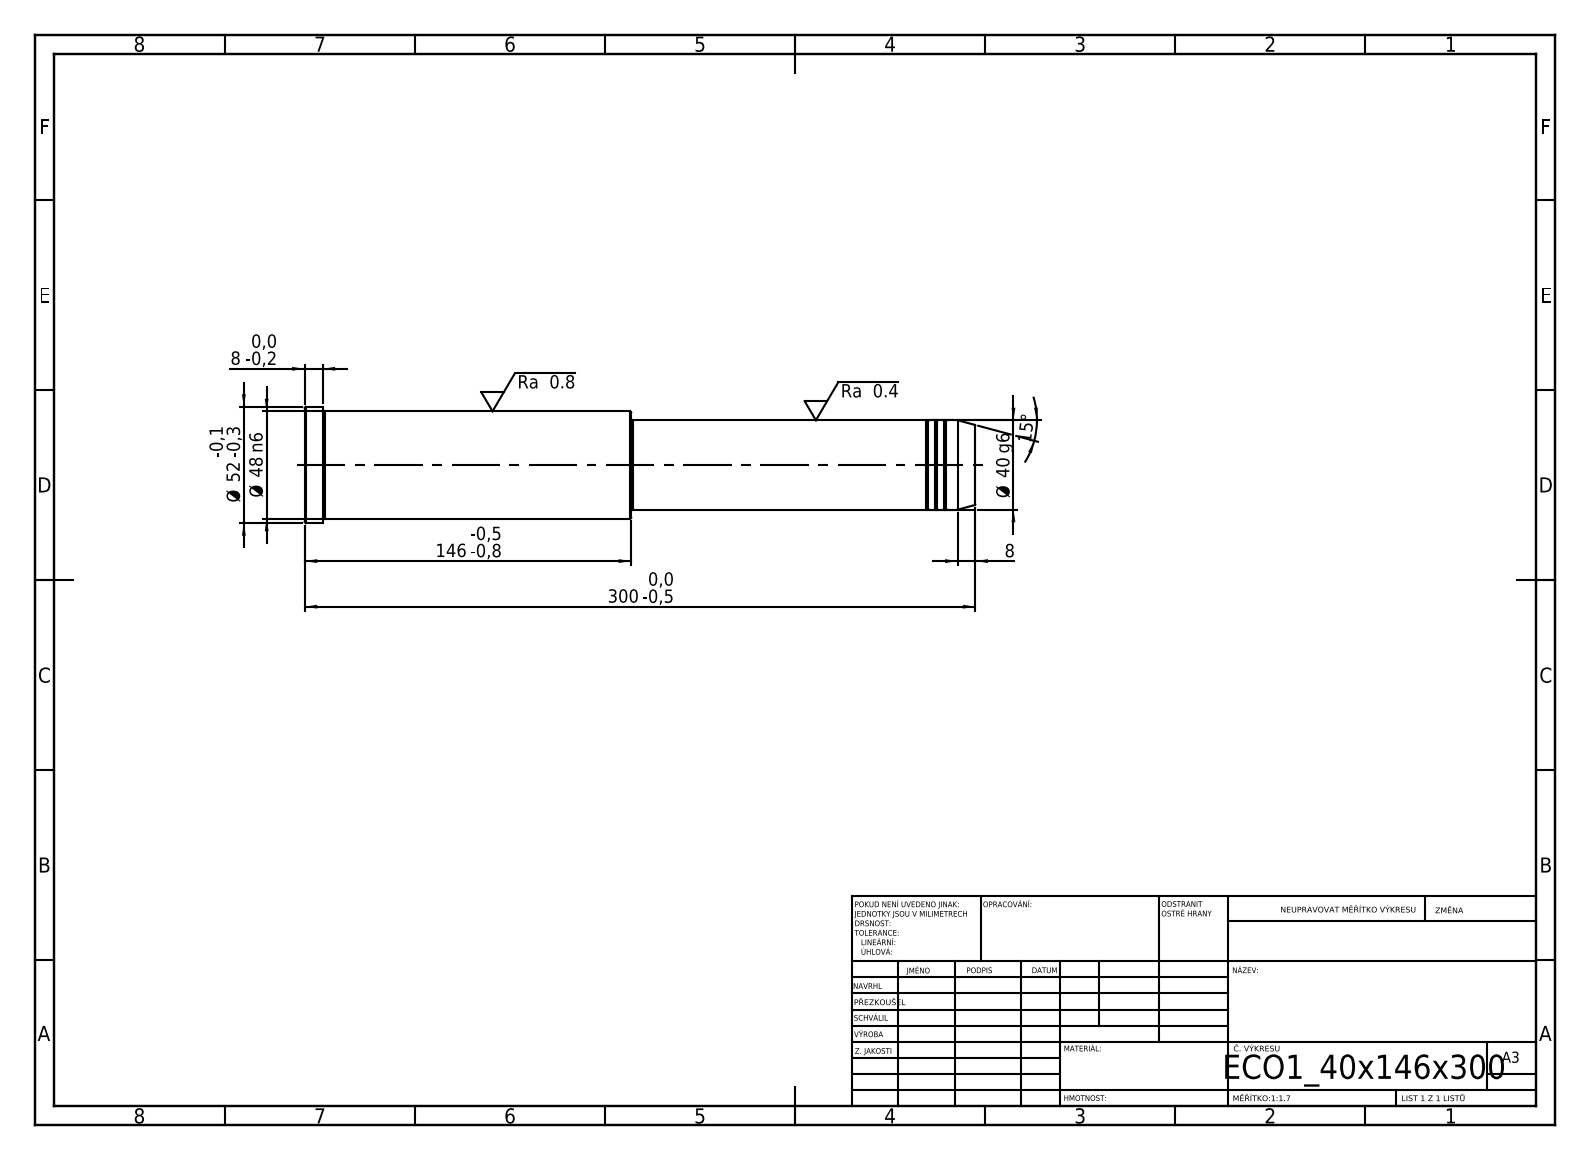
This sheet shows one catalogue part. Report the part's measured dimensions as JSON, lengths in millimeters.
{"step_written_by": "SolidWorks 2019 (CONFIG_CONTROL_DESIGN)", "units": "millimeters", "bodies": {"solids": 1, "faces": 43, "planar": 5, "cylindrical": 14, "other": 24}, "overall_size": [300, 52, 52], "volume_mm3": 458882, "surface_area_mm2": 45745, "round_bosses_or_shafts": [[52, 1], [48, 1], [40, 1], [39, 1]], "face_to_face_distances": [300, 154, 146, 292, 138, 8, 153, 1, 139, 147]}
